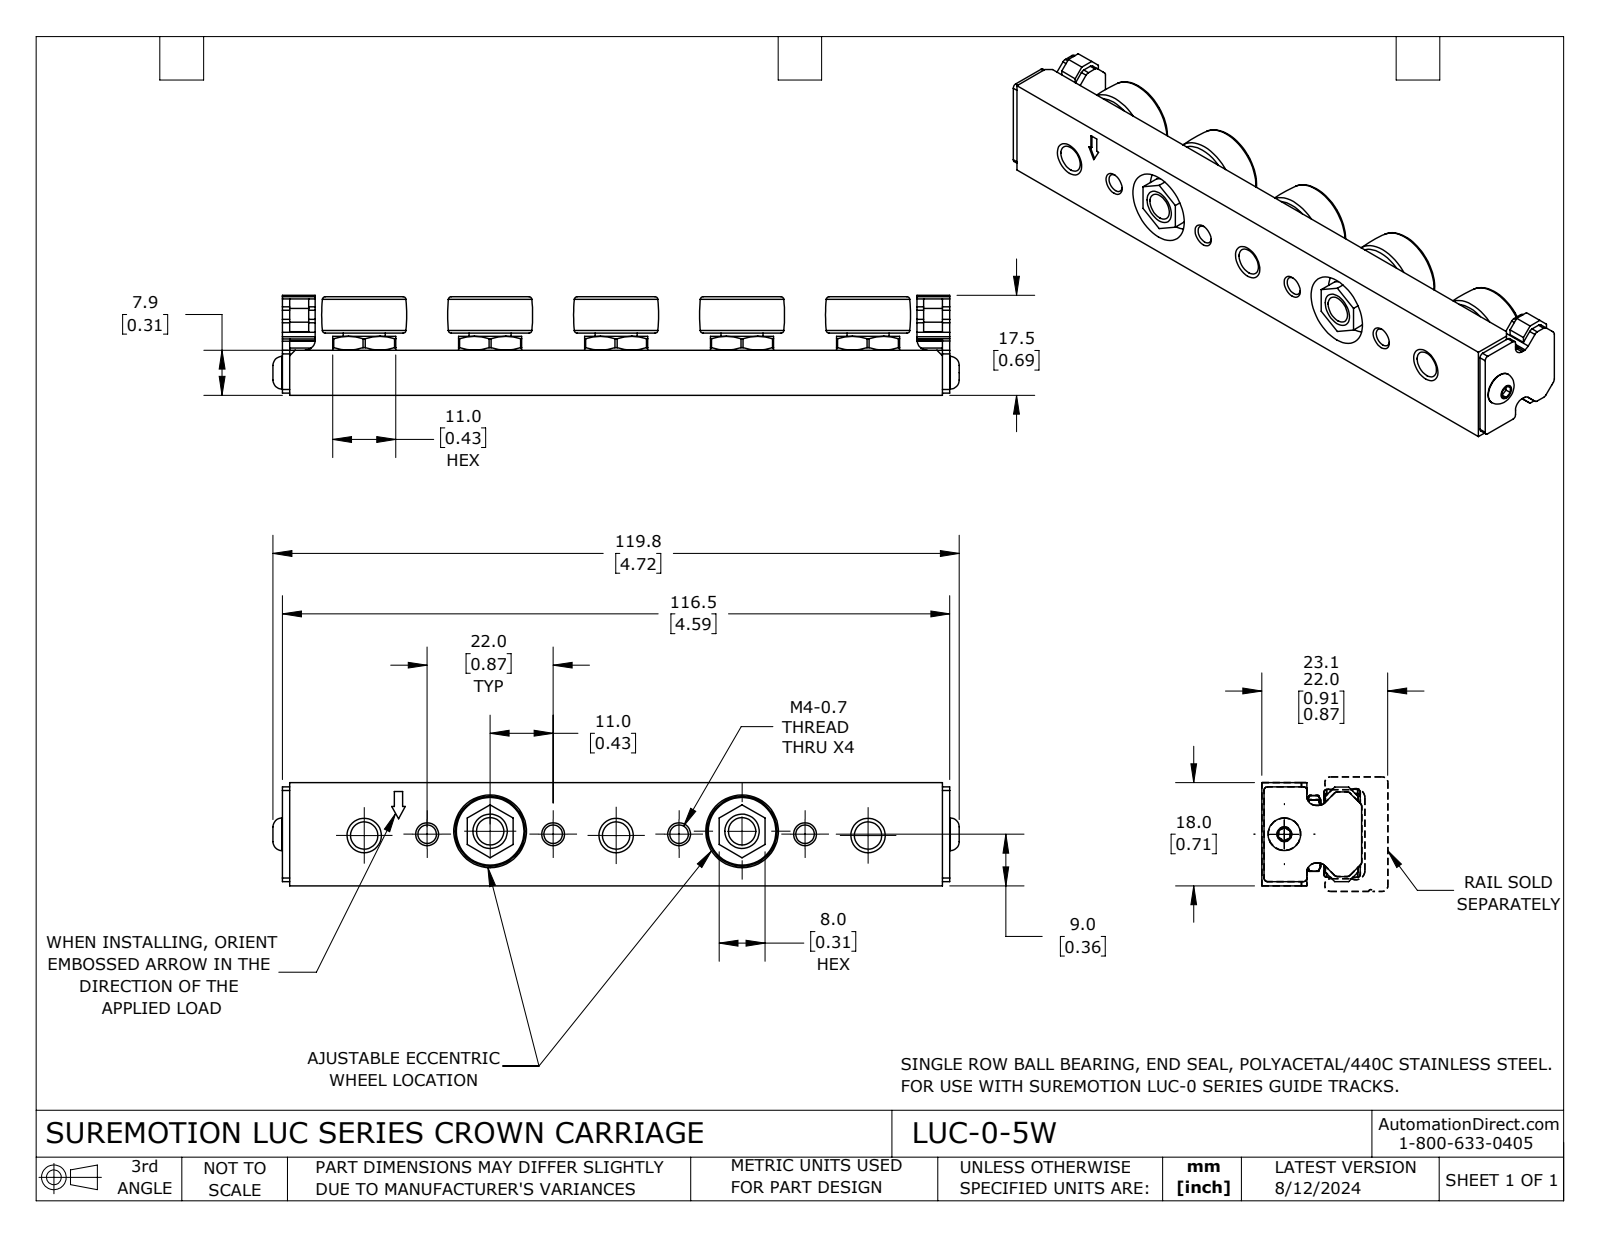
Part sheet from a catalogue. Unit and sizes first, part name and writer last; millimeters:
Units: millimetres
Overall size (bounding box): 119.8 × 18 × 17.4
Round holes (diameter × count): ⌀9.9 ×5, ⌀3.3 ×4, ⌀4.9 ×4, ⌀5.6 ×2, ⌀12.7 ×2, ⌀2.5 ×1, ⌀4.9 ×1
Round bosses / shafts (diameter × count): ⌀7.3 ×5, ⌀6 ×5, ⌀4.5 ×5, ⌀11.8 ×2, ⌀5.7 ×1, ⌀3 ×1
Partial cylindrical surfaces — rounded edges, fillets, slot ends (radius × count): R0.4 ×12, R0.8 ×6, R6.2 ×5, R0.6 ×4, R1.6 ×4, R1.8 ×2
Main face-to-face distances: 7.9, 18, 5.3, 1.1, 1.3, 115.3, 8.3, 16.1, 6.4, 11
Hole centre spacings: 11, 33, 44, 55, 22, 11, 22, 22
Volume: 23 220 mm³ · Surface area: 14 950 mm²
Bodies: 10 solids, 627 faces (233 planar, 188 cylindrical, 206 other)
Part name (STEP PRODUCT): LUC-0-5W
STEP written by: SolidWorks 2023 (CONFIG_CONTROL_DESIGN)
